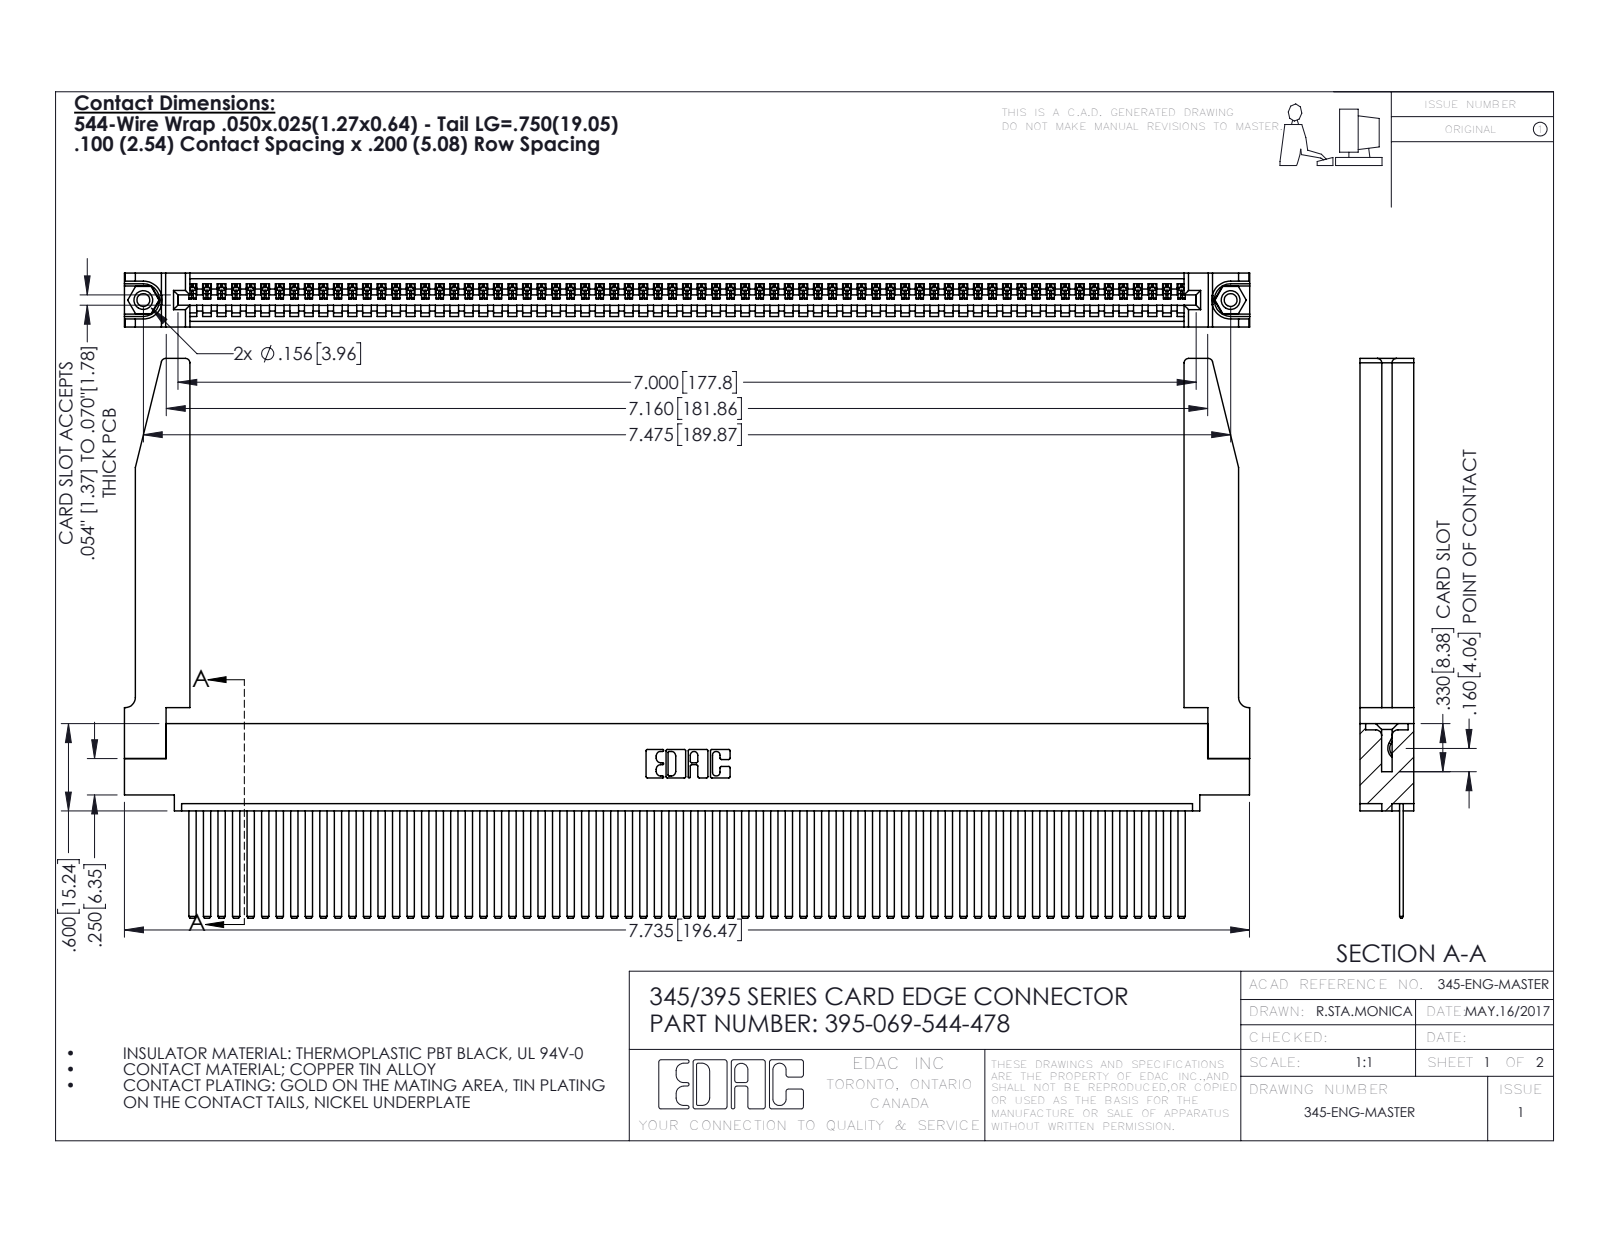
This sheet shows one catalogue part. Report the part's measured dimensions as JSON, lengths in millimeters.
{"part_name": "345-220-078_345-220-078; 395-069-544-478; 345-250-001_345-250-001-102; 345 Part_0.110 Offset - 0.156 Dia-TH (+1 more)", "step_written_by": "SolidWorks 2016 (CONFIG_CONTROL_DESIGN)", "units": "millimeters", "bodies": {"solids": 74, "faces": 3952, "planar": 2710, "cylindrical": 1190, "other": 52}, "overall_size": [196.5, 97.7, 9.4], "volume_mm3": 27380, "surface_area_mm2": 35750, "round_holes": [[2.3, 2], [3.2, 2], [4, 2], [1.6, 1]], "round_bosses_or_shafts": [[3.9, 2]], "partial_cylinders_radius": [[0.2, 138], [0.3, 22], [0.8, 8], [0.2, 6], [0.8, 6], [0.7, 3], [0.8, 2], [1, 2]], "face_to_face_distances": [1.8, 7.6, 9.4, 2.5, 6.9, 0.6, 5.1, 5.7, 3.8, 3.8], "hole_center_spacings": [6.9, 183.9, 189.9]}
